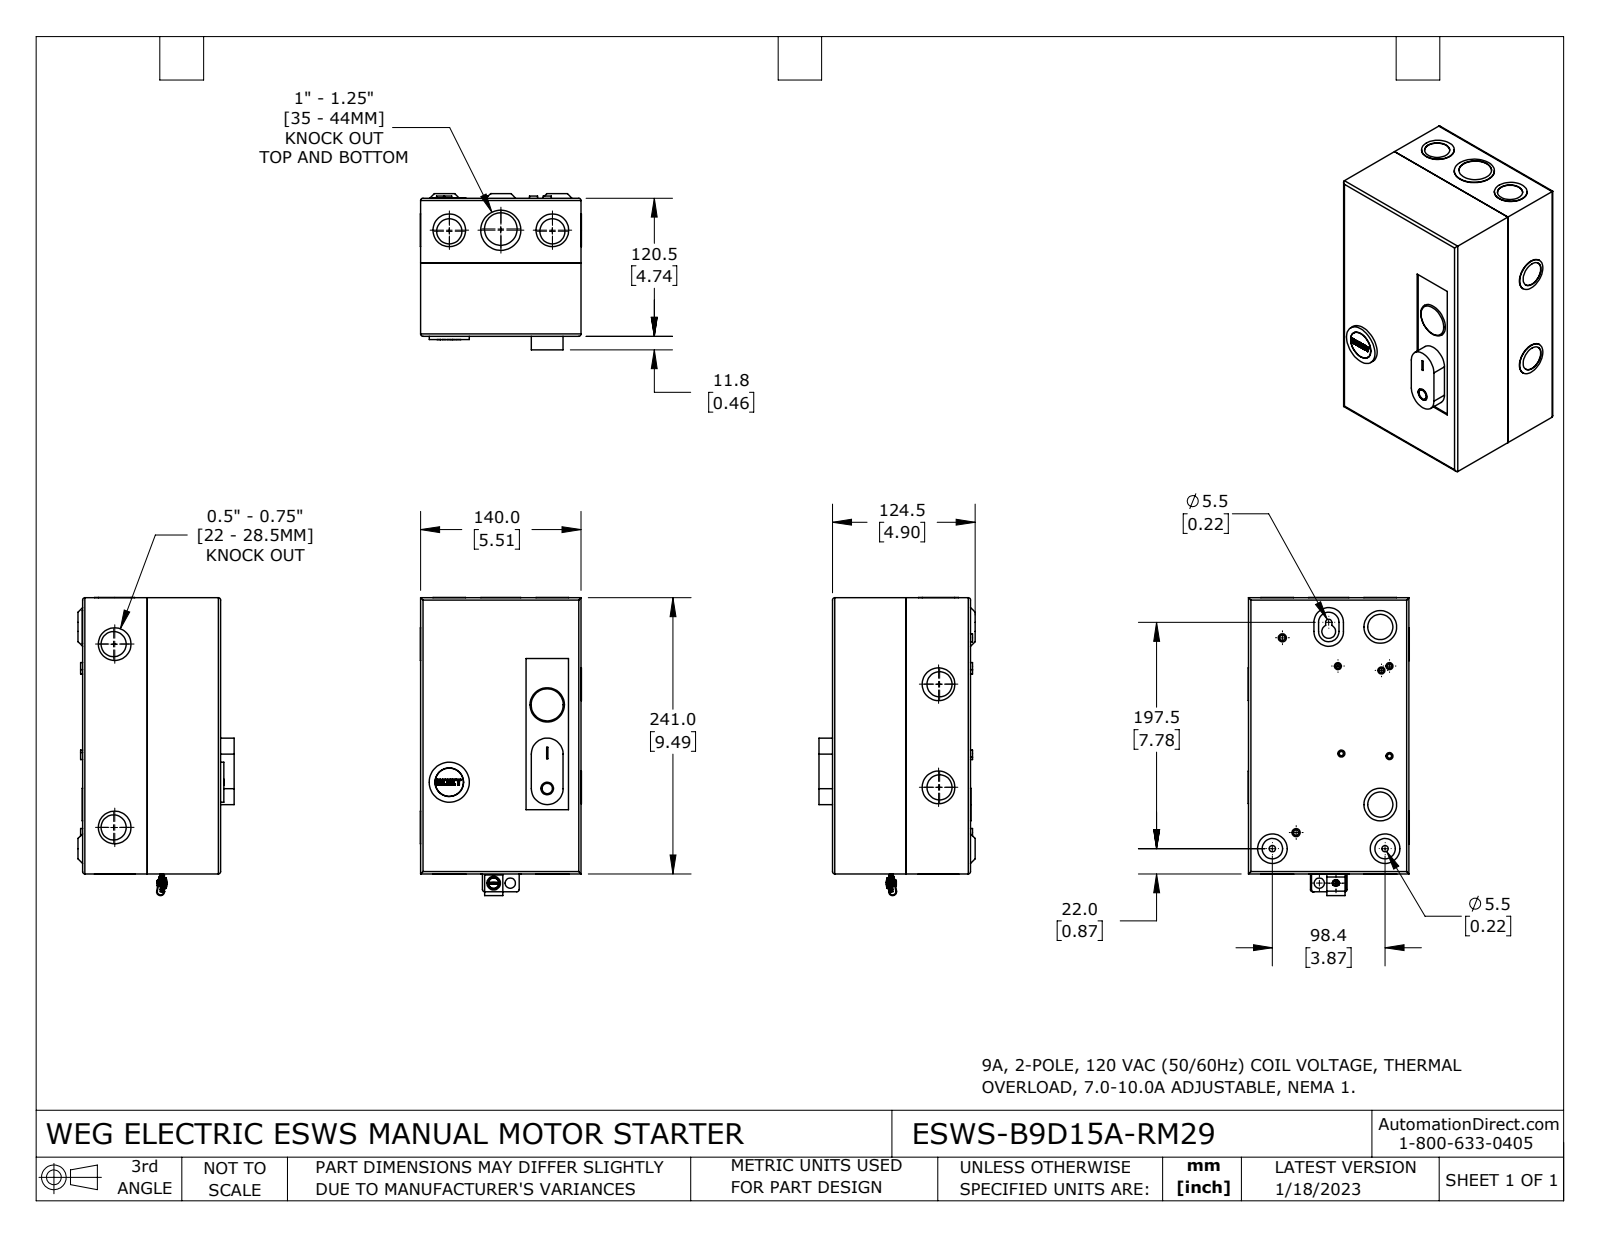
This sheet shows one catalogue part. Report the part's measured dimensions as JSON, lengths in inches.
{"part_name": "ESWS-B9D15A-RM29", "step_written_by": "SolidWorks 2021 (CONFIG_CONTROL_DESIGN)", "units": "inches", "bodies": {"solids": 7, "faces": 435, "planar": 168, "cylindrical": 230, "other": 37}, "overall_size": [10.248, 5.535, 5.366], "volume_in3": 16.23, "surface_area_in2": 585.2, "round_holes": [[0.146, 5], [0.864, 4], [0.183, 2], [0.217, 2], [0.354, 2], [0.864, 2], [0.866, 2], [0.886, 2], [0.256, 1], [0.303, 1], [0.433, 1], [0.469, 1]], "round_bosses_or_shafts": [[1.124, 6], [0.24, 5], [1.122, 2], [0.278, 2], [1.38, 1], [1.378, 1], [1.193, 1], [1.148, 1]], "partial_cylinders_radius": [[0.004, 34], [0.079, 13], [0.031, 4], [0.108, 3], [0.059, 2], [0.075, 2], [0.122, 2], [0.138, 2]], "face_to_face_distances": [0.047, 4.697, 5.465, 4.65, 9.441, 4.744, 5.417, 5.512, 0.071, 0.063], "hole_center_spacings": [0.571, 1.378, 1.773, 3.387, 3.543, 4.921, 5.995, 7.484]}
